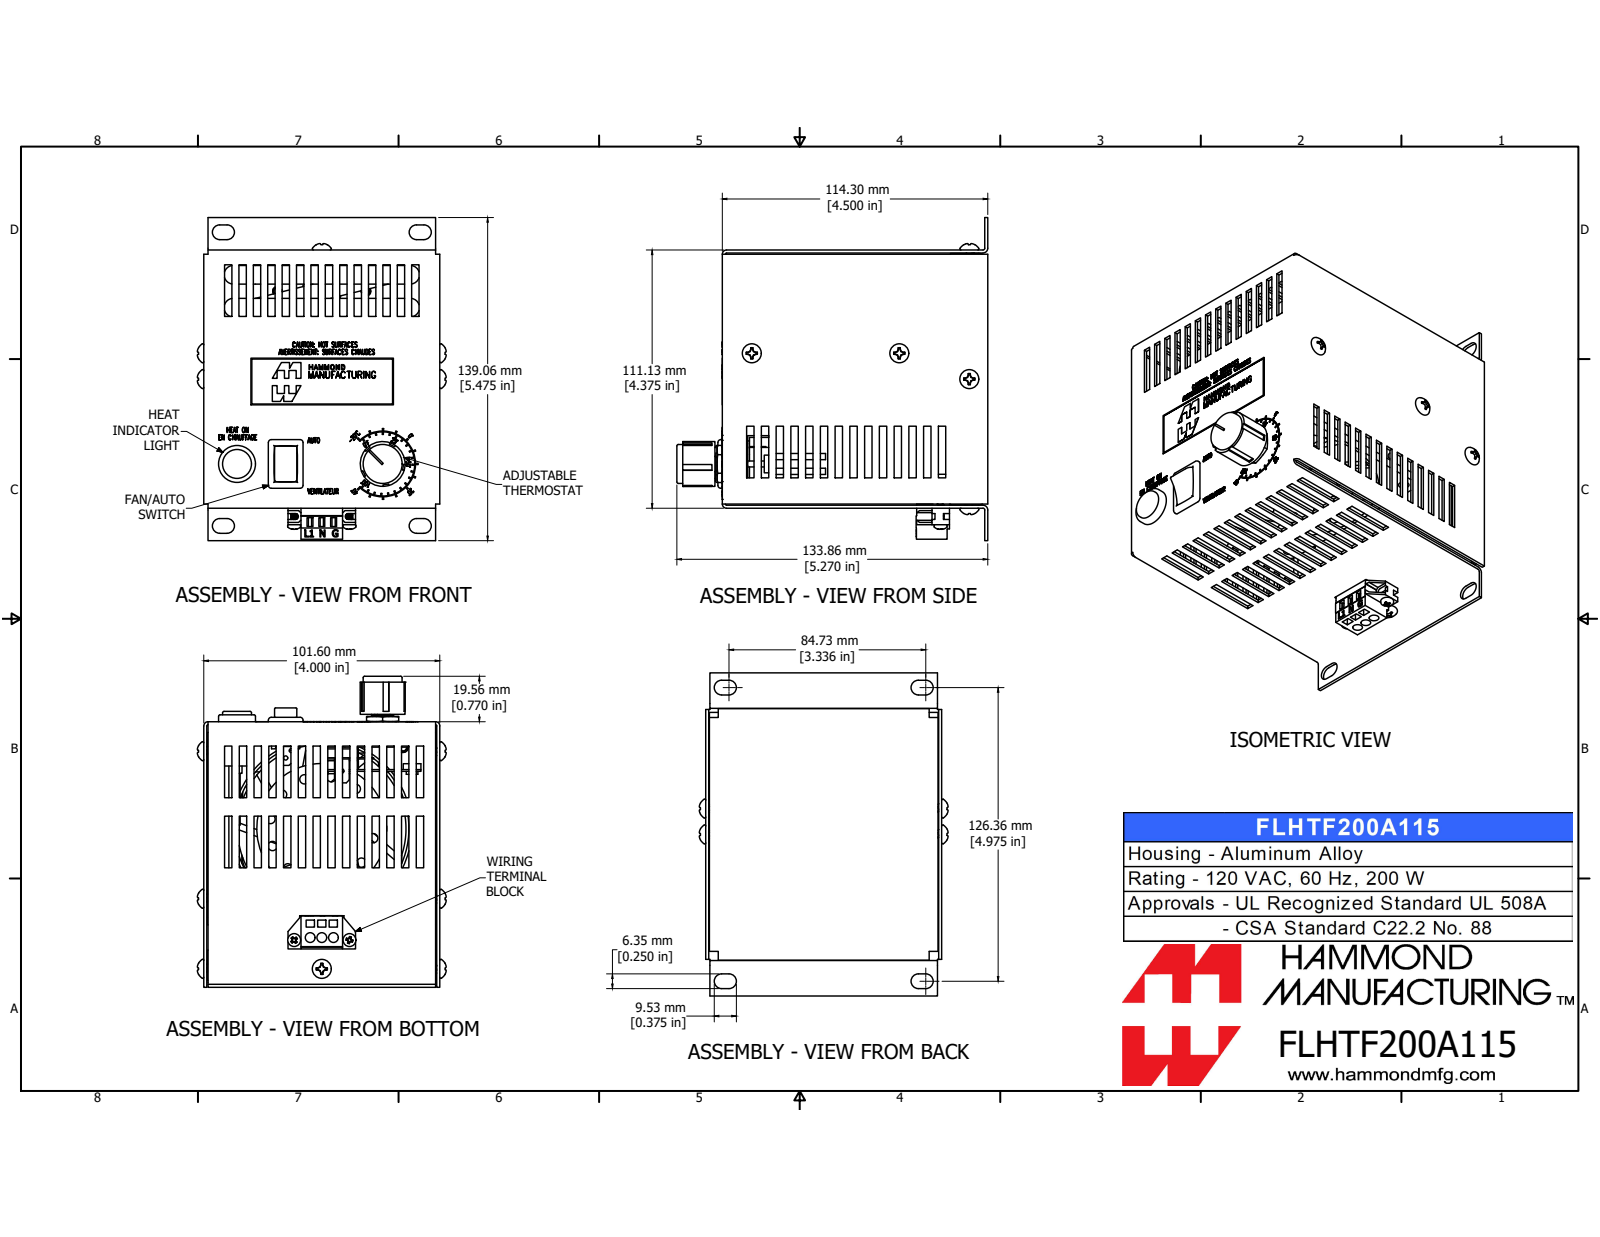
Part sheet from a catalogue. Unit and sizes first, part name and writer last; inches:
Units: inches
Overall size (bounding box): 5.475 × 5.27 × 4.218
Round holes (diameter × count): ⌀0.137 ×4, ⌀0.182 ×4, ⌀0.203 ×4, ⌀0.165 ×3, ⌀0.085 ×2, ⌀0.12 ×2, ⌀0.13 ×2, ⌀0.189 ×2, ⌀0.066 ×1, ⌀0.07 ×1, ⌀0.25 ×1, ⌀0.383 ×1
Round bosses / shafts (diameter × count): ⌀0.164 ×4, ⌀0.104 ×4, ⌀0.17 ×2, ⌀0.105 ×2, ⌀0.76 ×1, ⌀0.66 ×1, ⌀0.65 ×1, ⌀0.625 ×1
Partial cylindrical surfaces — rounded edges, fillets, slot ends (radius × count): R0.125 ×38, R0.05 ×17, R0.025 ×12, R0.629 ×12, R0.15 ×9, R0.02 ×4, R0.071 ×4, R0.015 ×2
Main face-to-face distances: 0.051, 3.949, 0.1, 0.051, 4.324, 4, 3.898, 4.494, 4.394, 4.443
Hole centre spacings: 2.756, 0.197, 0.275, 0.471, 0.531, 0.564, 0.565, 0.667
Volume: 8.774 in³ · Surface area: 274 in²
Bodies: 17 solids, 4140 faces (3640 planar, 274 cylindrical, 226 other)
Part name (STEP PRODUCT): FLHTF200A115
STEP written by: SolidWorks 2019 (AUTOMOTIVE_DESIGN)
